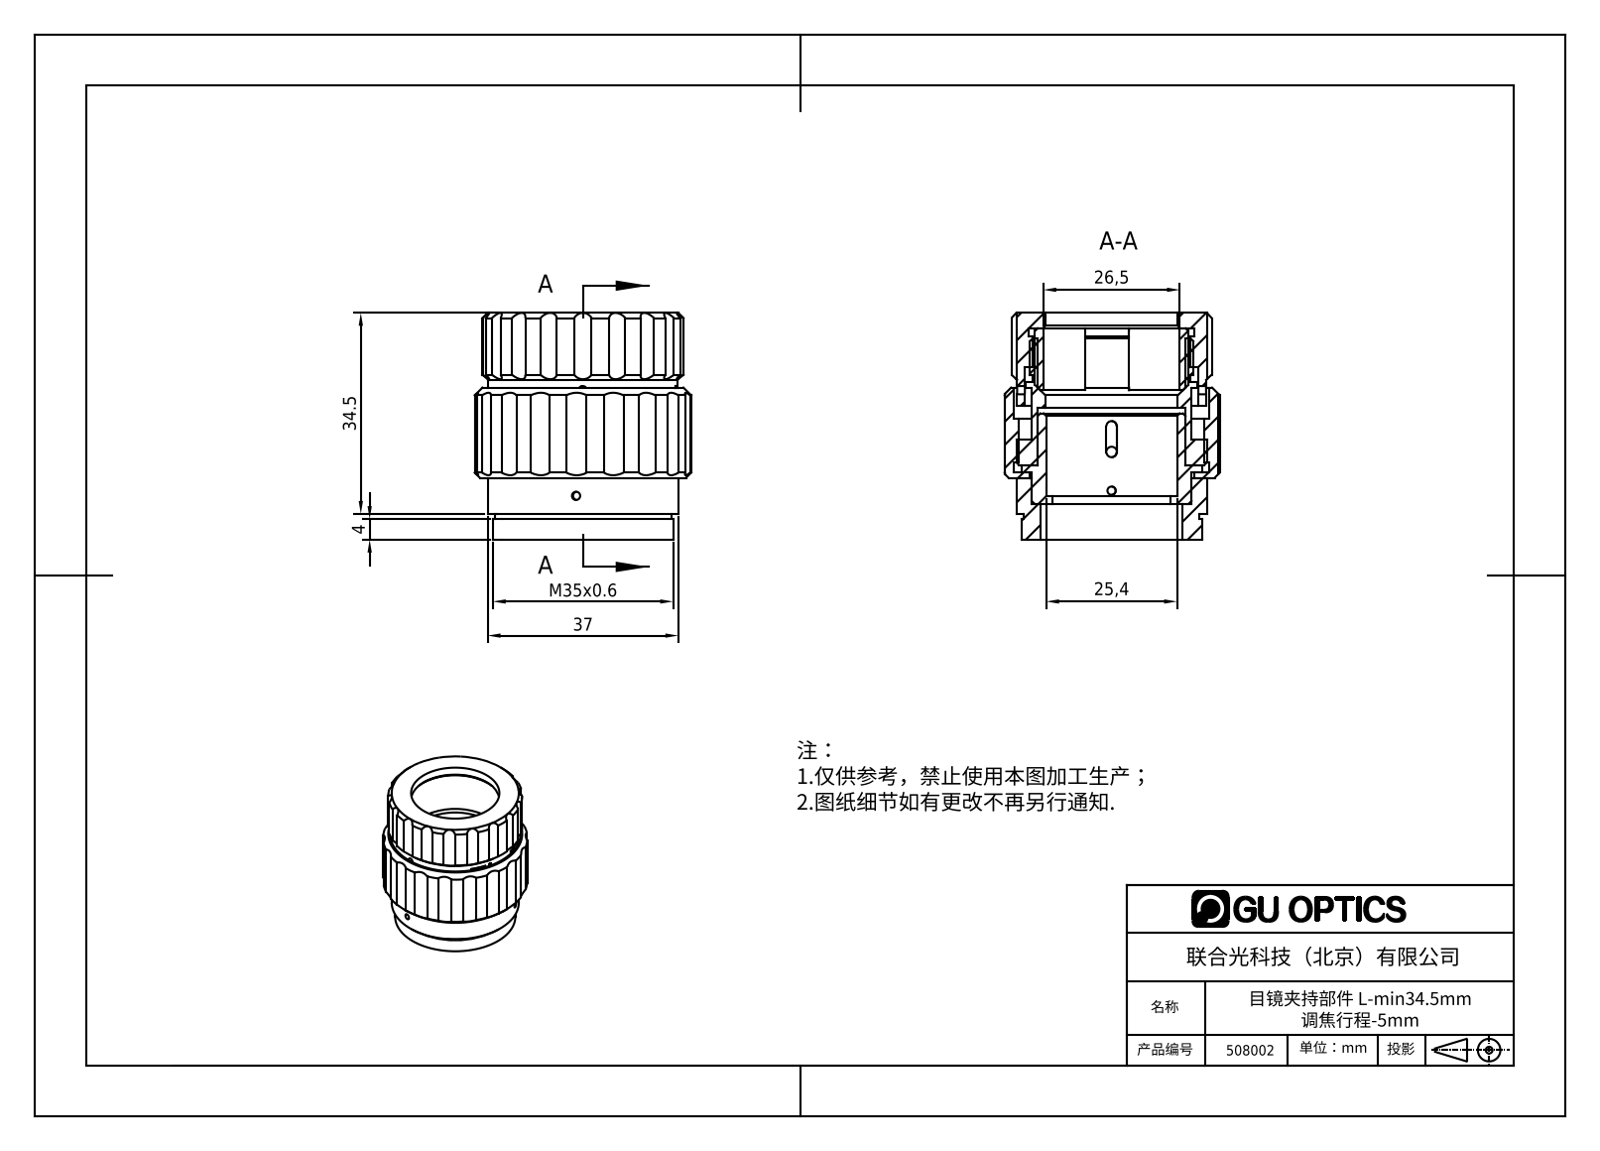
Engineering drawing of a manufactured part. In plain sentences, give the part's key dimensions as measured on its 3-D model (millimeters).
The part is named "508002". Its 3-D file was written by "SolidWorks 2020 (CONFIG_CONTROL_DESIGN)". It is 6 solids with 254 faces: 35 planar, 178 cylindrical and 41 other. Overall it measures 44 by 42 by 41.98 millimeters. Its volume is 25 779 cubic millimeters and its surface area 26 653 square millimeters. Round holes: 7 of diameter 1.6, 1 of diameter 2.05, 1 of diameter 23, 1 of diameter 25.4, 1 of diameter 25.7, 1 of diameter 26.5, 1 of diameter 27.5, 1 of diameter 28.65, 1 of diameter 28.7, 1 of diameter 30.7, 1 of diameter 32, 1 of diameter 32.2. Round bosses or shafts: 1 of diameter 37, 1 of diameter 36.7, 1 of diameter 35, 1 of diameter 34.2, 1 of diameter 33.2, 1 of diameter 31.7, 1 of diameter 31, 1 of diameter 29.7. Partial cylindrical surfaces (rounded edges, fillets, slot ends): 18 of radius 2, 18 of radius 5, 2 of radius 1, 1 of radius 19.5, 1 of radius 21. The main face-to-face distances are 5, 7.5, 6, 14.5, 2.5, 1, 1.5, 29.5, 24.5, 32.
